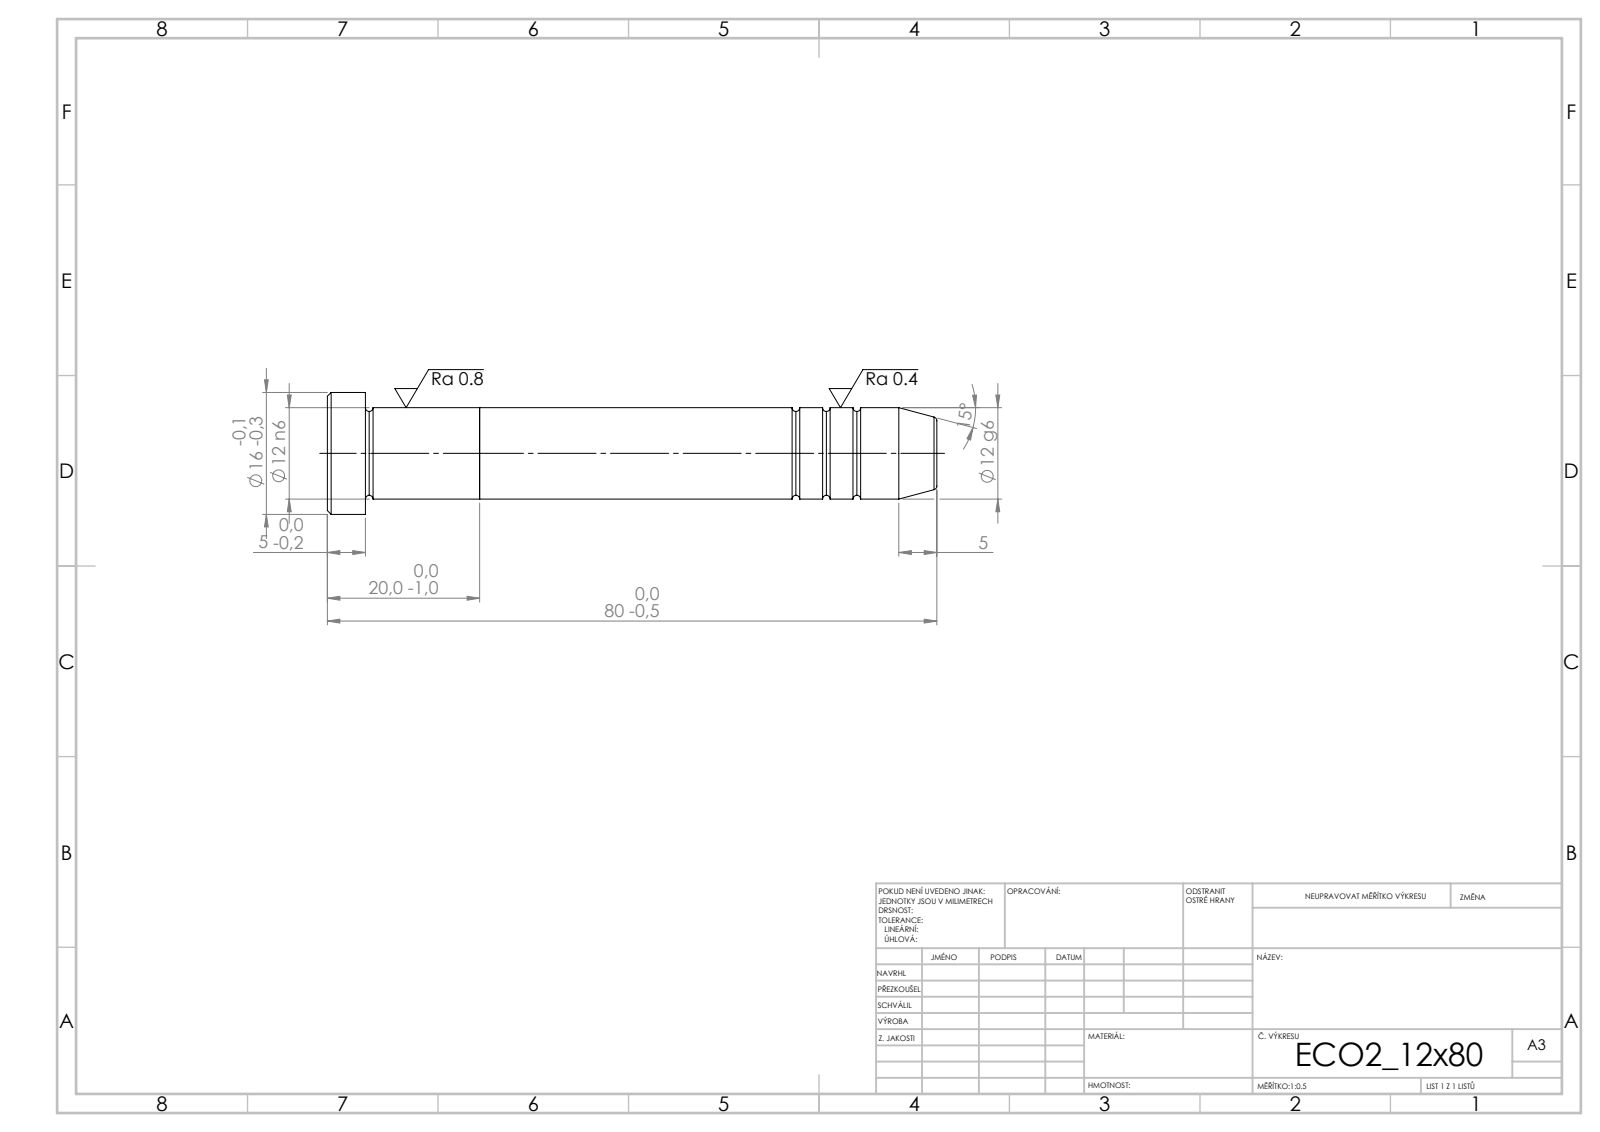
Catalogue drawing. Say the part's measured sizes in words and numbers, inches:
Its 3-D file was written by "SolidWorks 2019 (CONFIG_CONTROL_DESIGN)". It is 2 solids with 39 faces: 5 planar, 12 cylindrical and 22 other. Overall it measures 3.15 by 0.63 by 0.63 inches. Its volume is 0.568 cubic inches and its surface area 5.738 square inches. Round bosses or shafts: 1 of diameter 0.63, 1 of diameter 0.472. The main face-to-face distances are 0.787, 0.591, 0.197, 2.362, 2.953, 3.15.
